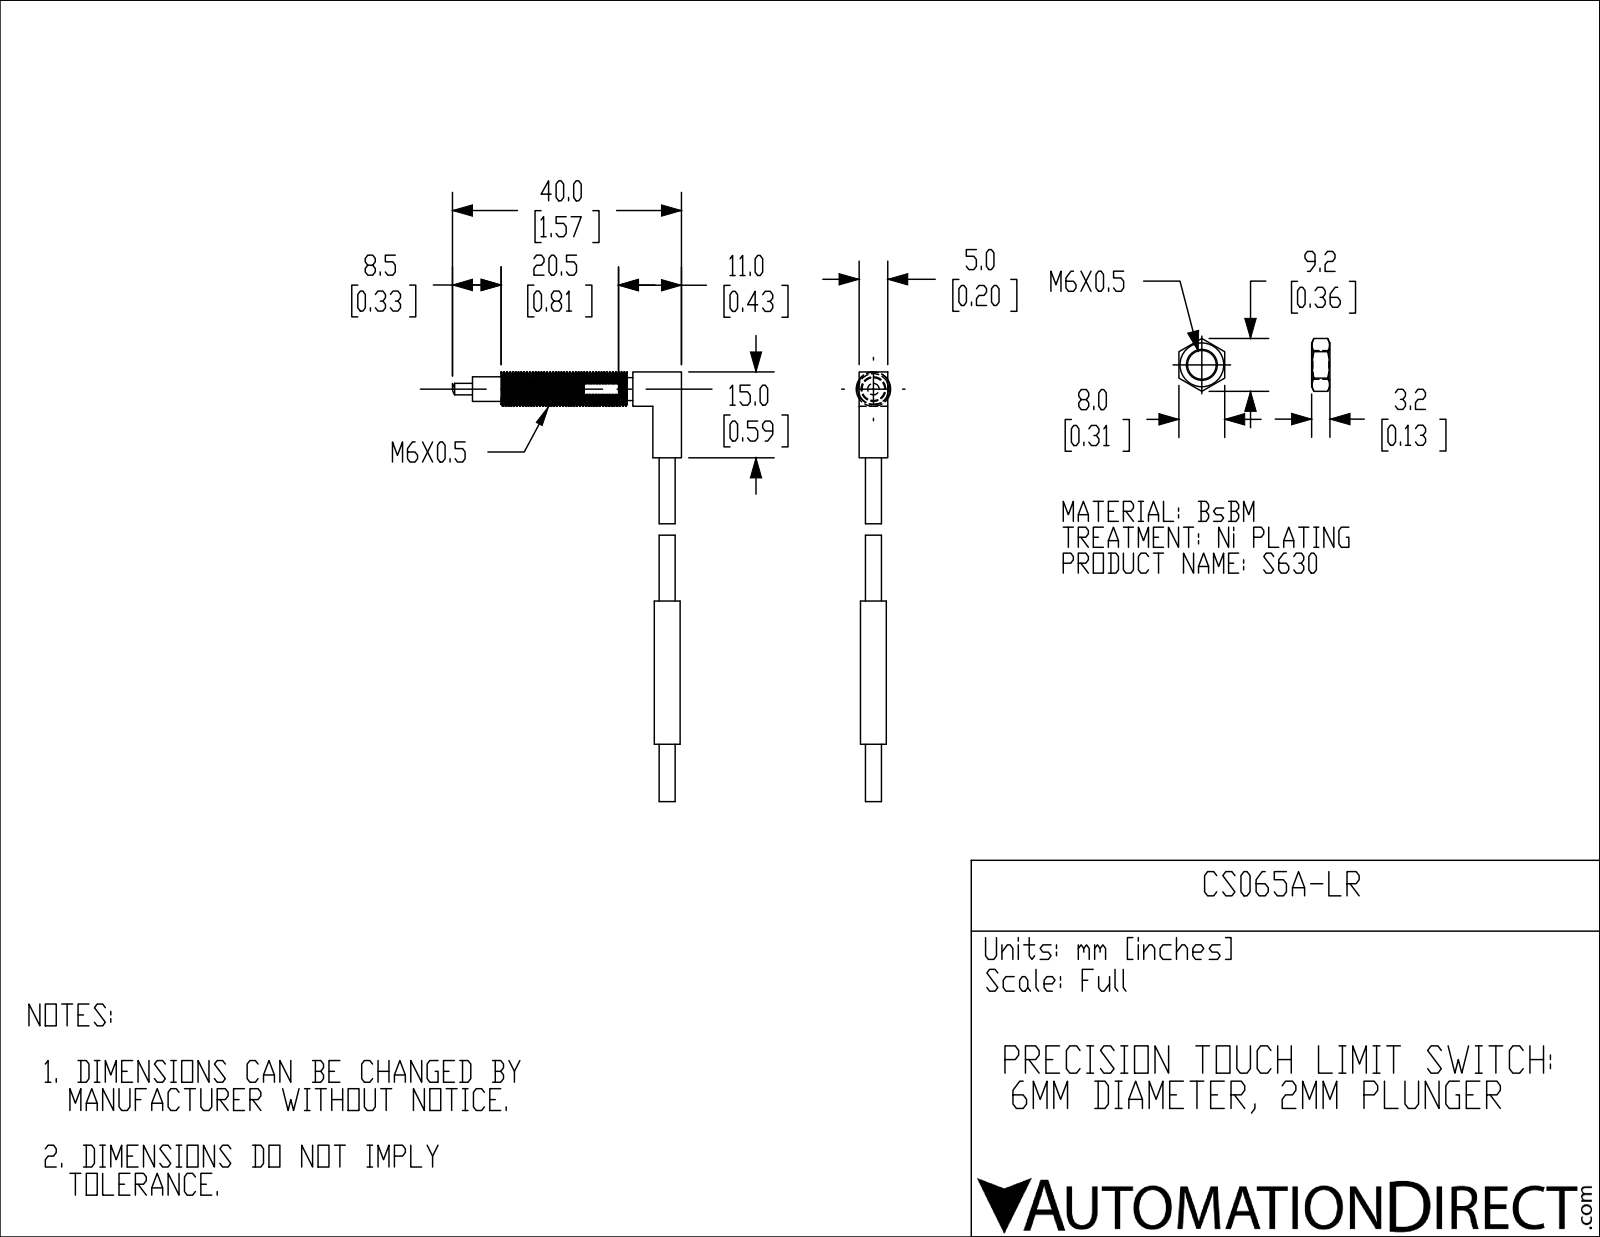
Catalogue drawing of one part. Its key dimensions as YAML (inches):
part_name: "CS065A-LR"
step_written_by: "SolidWorks 2018 (AUTOMOTIVE_DESIGN)"
units: inches
bodies: {solids: 2, faces: 31, planar: 22, cylindrical: 8, other: 1}
overall_size: [2.953, 1.575, 0.236]
volume: 0.109
surface_area: 2.559
round_bosses_or_shafts:
  - {diameter: 0.236, count: 1}
  - {diameter: 0.177, count: 1}
  - {diameter: 0.169, count: 1}
  - {diameter: 0.157, count: 1}
  - {diameter: 0.11, count: 1}
  - {diameter: 0.079, count: 1}
face_to_face_distances: [0.197, 1.24, 0.236, 1.043, 0.335, 0.984, 0.591, 1.437, 0.354, 0.138]
